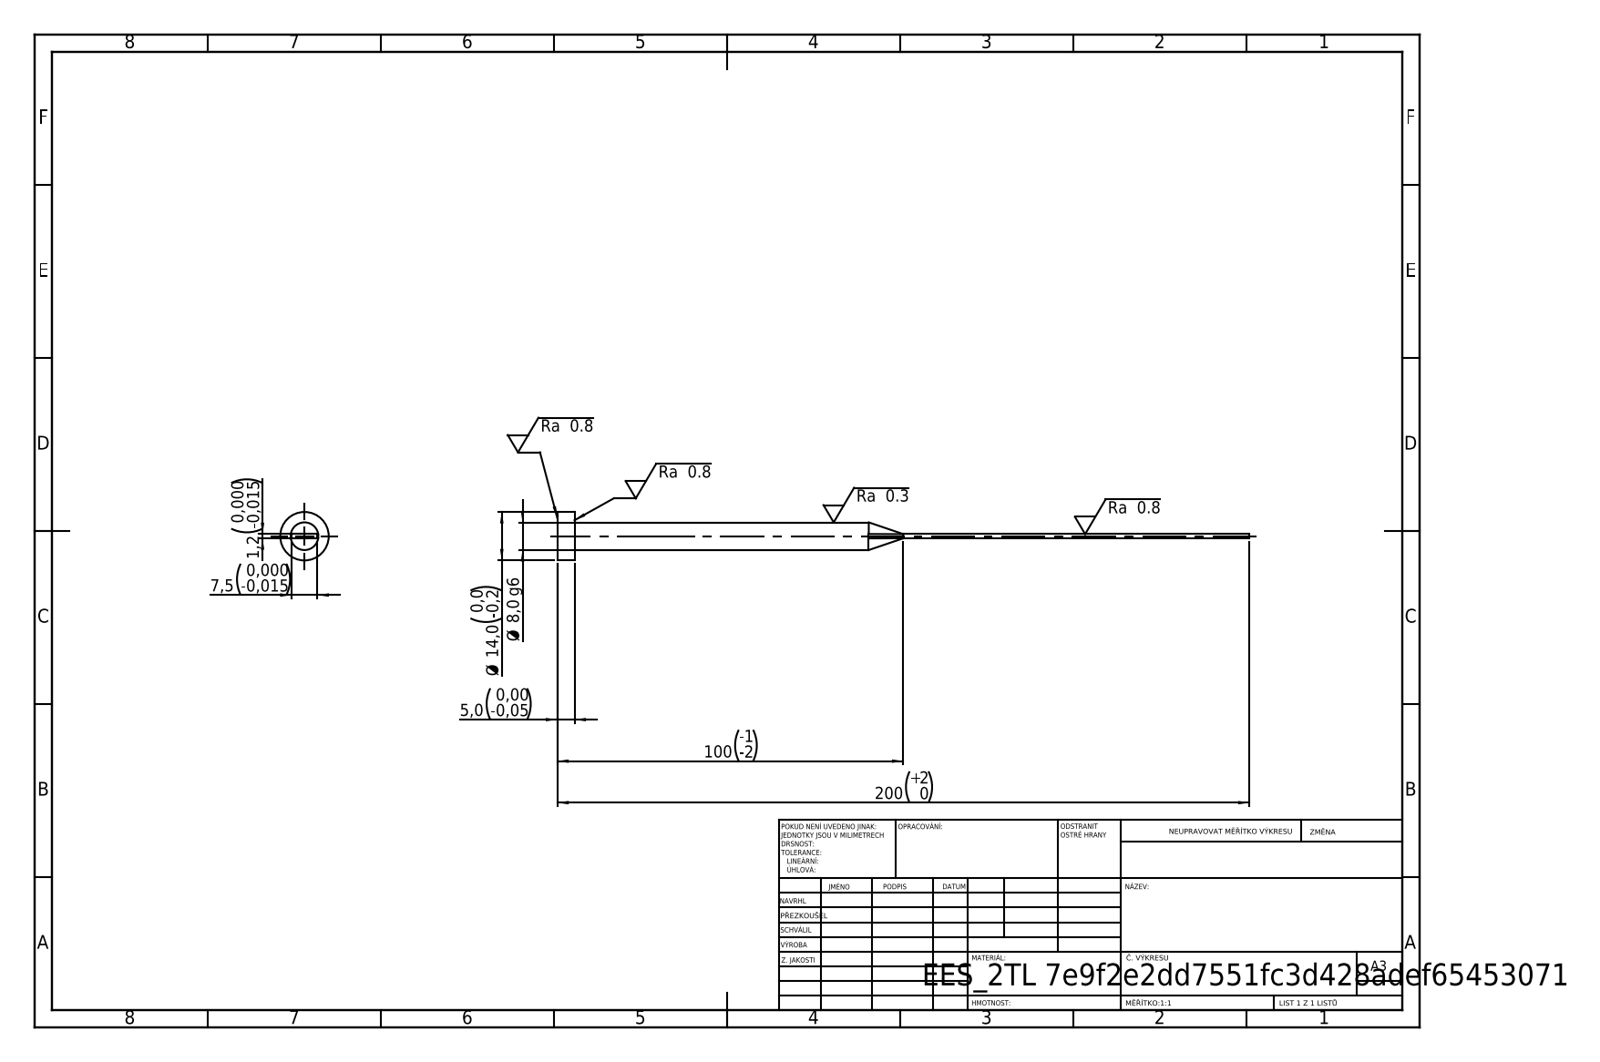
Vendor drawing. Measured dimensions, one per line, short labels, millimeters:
written by: SolidWorks 2019 (CONFIG_CONTROL_DESIGN)
unit: mm
bodies: 1 solid, 15 faces (7 planar, 4 cylindrical, 4 other)
size: 200 × 14 × 14
volume: 6 221 mm³; area: 4 570 mm²
bosses: 1× ⌀14, 1× ⌀8
face distances: 1.2, 7.5, 5, 200, 195
